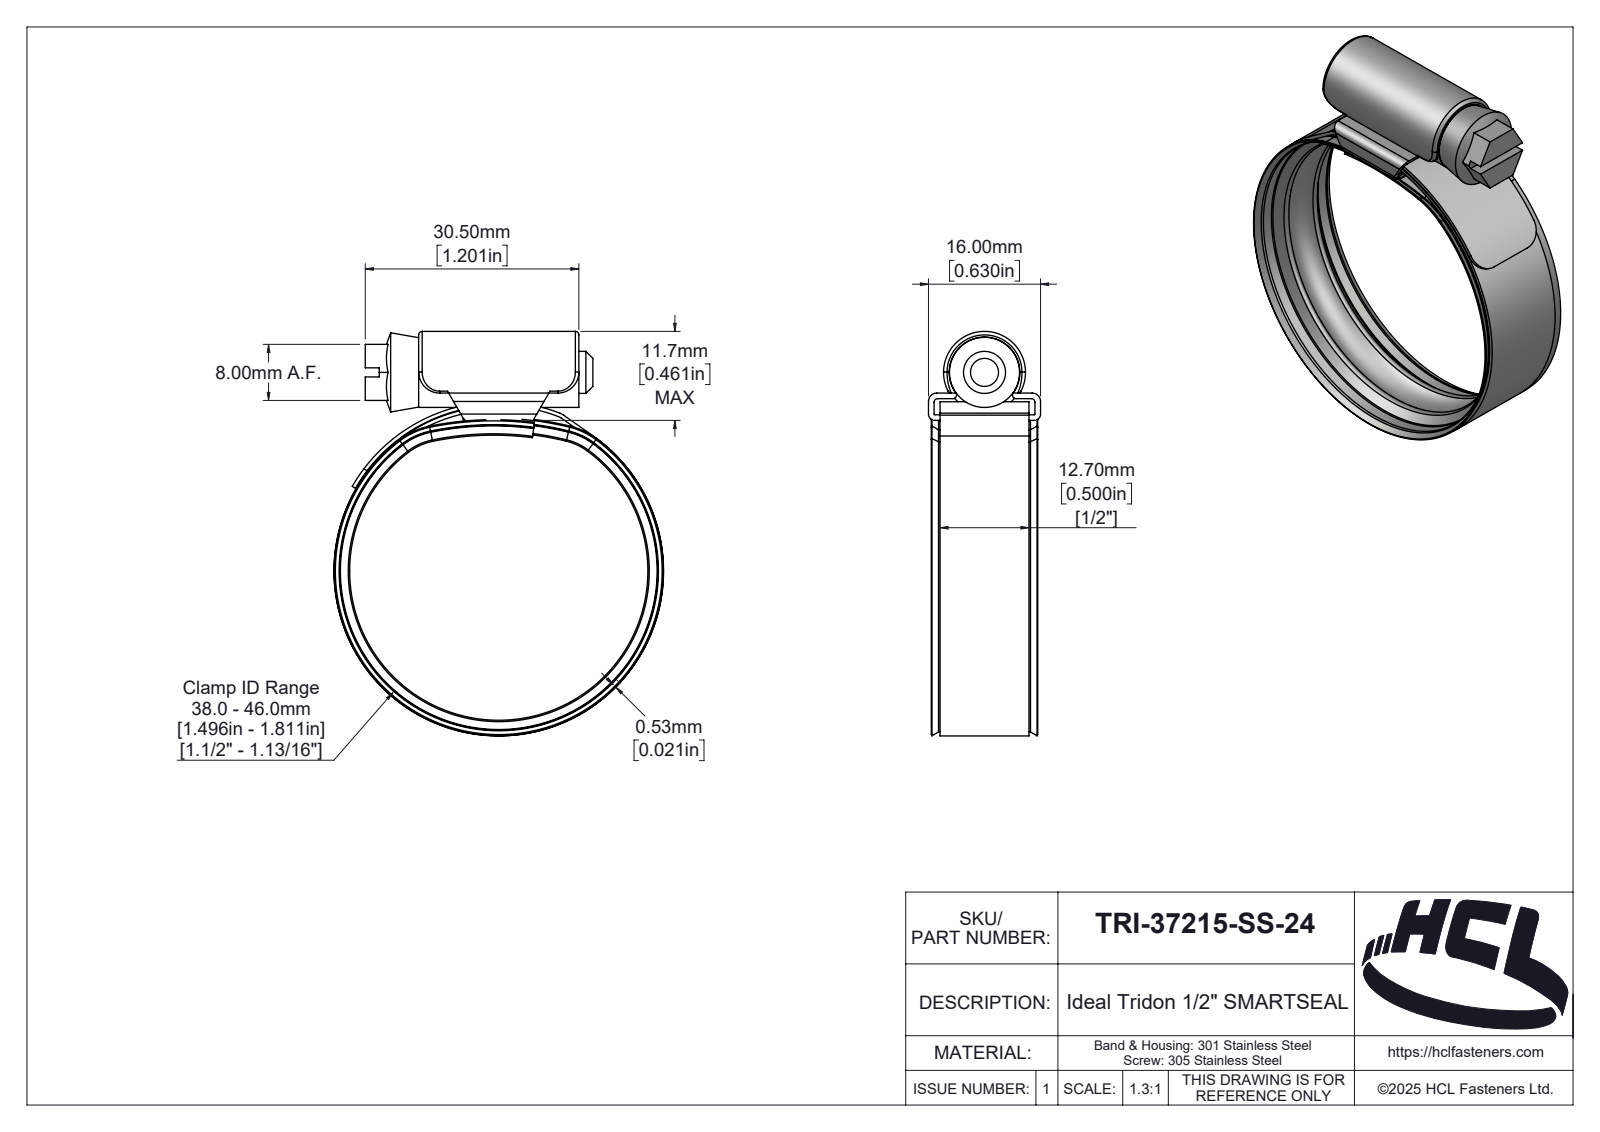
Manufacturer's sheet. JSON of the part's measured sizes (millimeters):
{"part_name": "TRI-37215-SS-24", "step_written_by": "SolidWorks 2025 (AUTOMOTIVE_DESIGN)", "units": "millimeters", "bodies": {"solids": 4, "faces": 418, "planar": 42, "cylindrical": 119, "other": 257}, "overall_size": [57.73, 47.06, 16], "volume_mm3": 4715, "surface_area_mm2": 12626, "round_holes": [[45.4, 1], [46, 1]], "round_bosses_or_shafts": [[47.06, 1], [45.8, 1], [10, 1], [6, 1]], "partial_cylinders_radius": [[0.5, 6], [3, 4], [0.1, 2], [0.9, 2], [1.2, 2], [9.9, 2], [10.1, 2], [0.46, 1]], "face_to_face_distances": [0.8, 3.1, 12.7, 2.3, 0.53, 30.5, 3.9, 1.65, 14.35, 15.2]}
